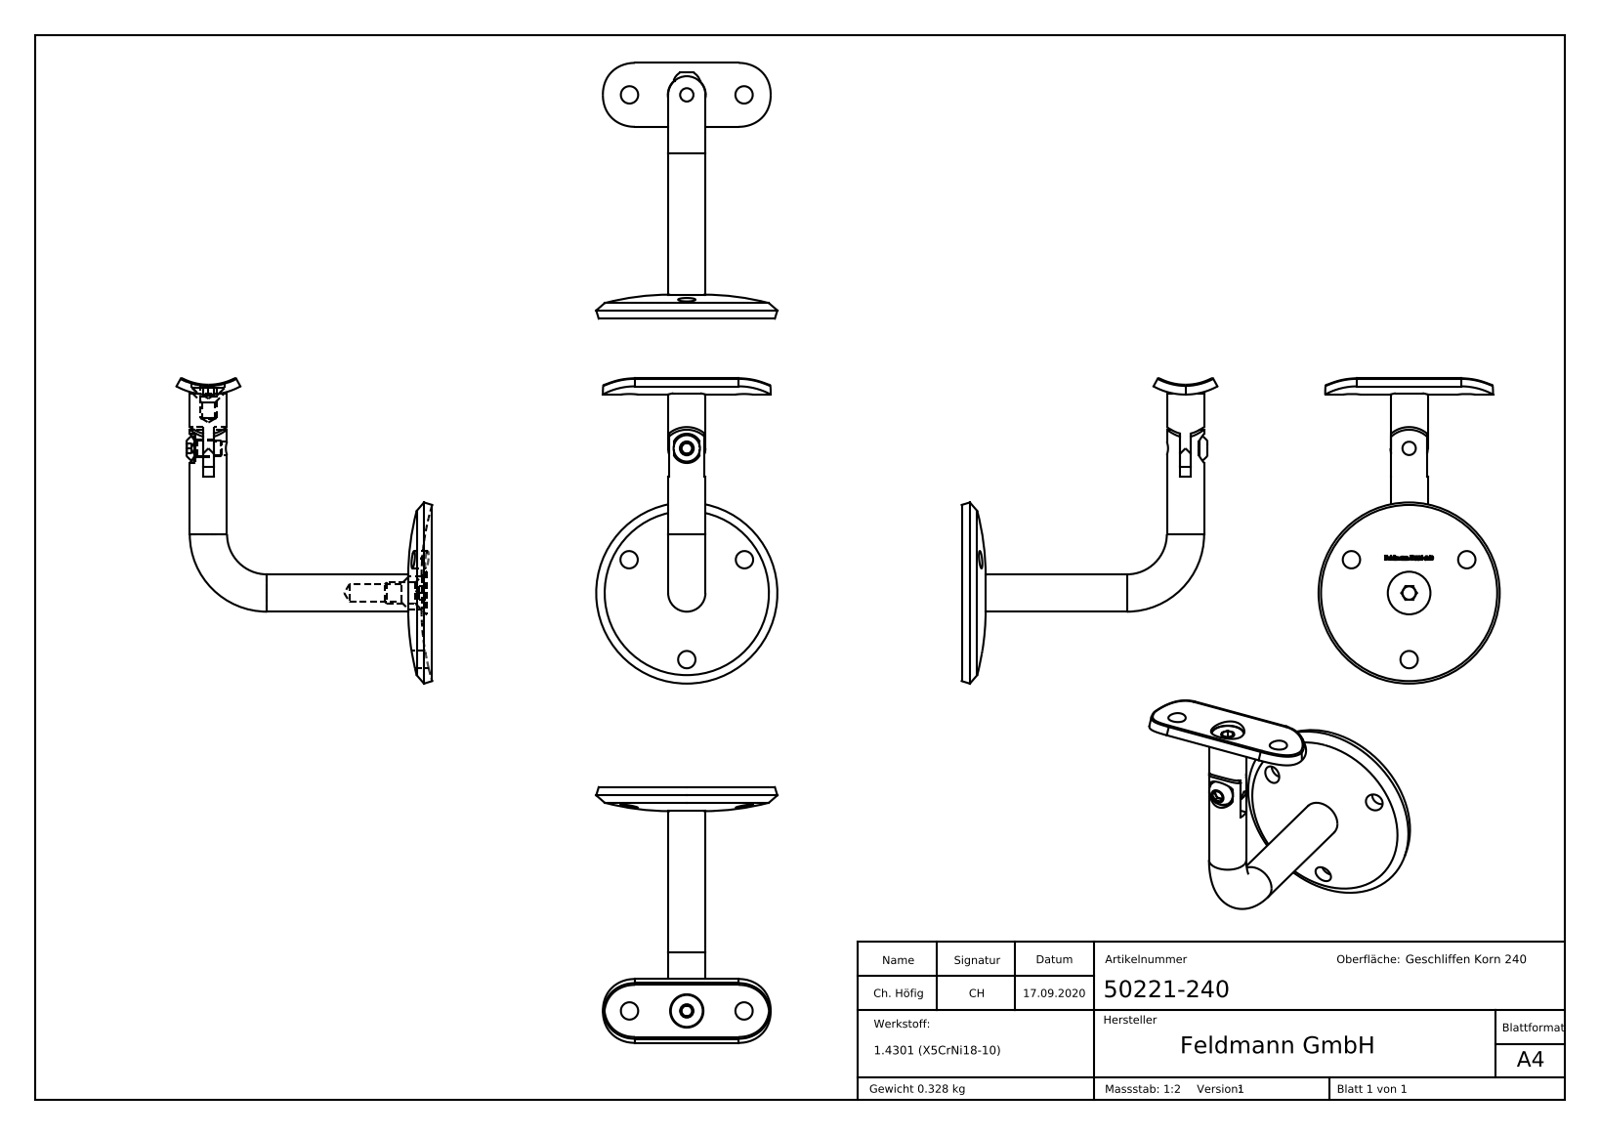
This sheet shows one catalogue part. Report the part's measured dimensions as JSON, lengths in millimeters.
{"part_name": "50221-240; 50221-240 Teil4_50221-240 Teil4 Keyshot; 50221-240 Teil3_50221-240 Teil3 Keyshot; DIN-7991 M3-M10_DIN7991 M6x12 Keyshot (+8 more)", "step_written_by": "SolidWorks 2018 (CONFIG_CONTROL_DESIGN)", "units": "millimeters", "bodies": {"solids": 7, "faces": 402, "planar": 56, "cylindrical": 167, "other": 179}, "overall_size": [114.64, 95.94, 67.97], "volume_mm3": 41844, "surface_area_mm2": 21825, "round_holes": [[6.5, 6], [5, 2], [12.5, 2], [6.8, 1]], "round_bosses_or_shafts": [[14, 2], [6, 2], [16, 1], [12, 1], [10.5, 1], [8, 1]], "partial_cylinders_radius": [[0.1, 18], [12, 4], [0.5, 2], [5.5, 1], [7, 1], [7.1, 1], [10, 1], [10.5, 1]], "face_to_face_distances": [4.05, 80, 4.1, 84.1, 4, 84.05, 80.05, 7.05, 3, 2.95], "hole_center_spacings": [25, 43.3, 21.5, 47.07, 43, 54.3, 79.3]}
